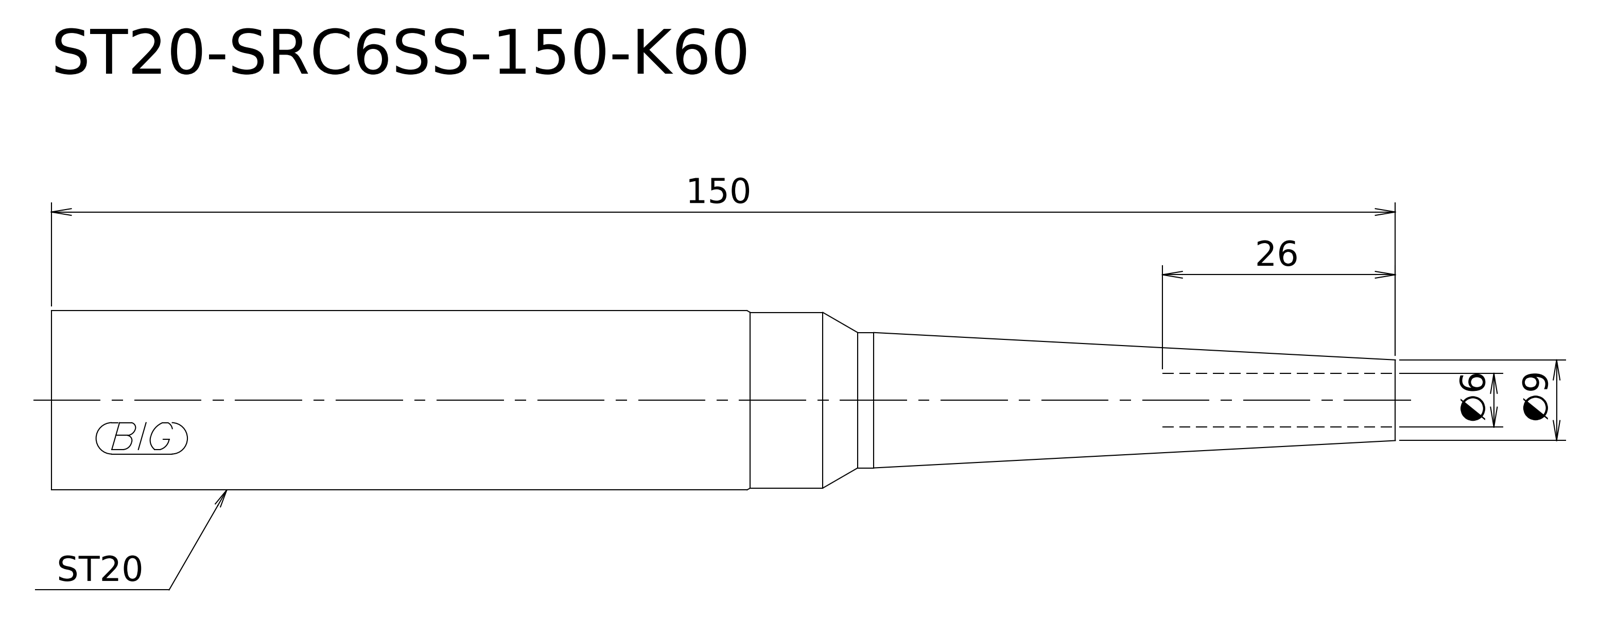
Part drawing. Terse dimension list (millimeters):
written by: Kubotek KeyCreator V8.5.1 (14335) (CONFIG_CONTROL_DESIGN)
unit: mm
bodies: 1 solid, 8 faces (2 planar, 3 cylindrical, 3 other)
size: 150 × 20 × 20
volume: 34 975 mm³; area: 8 318 mm²
bosses: 1× ⌀20, 1× ⌀19.6, 1× ⌀15.1
face distances: 150
